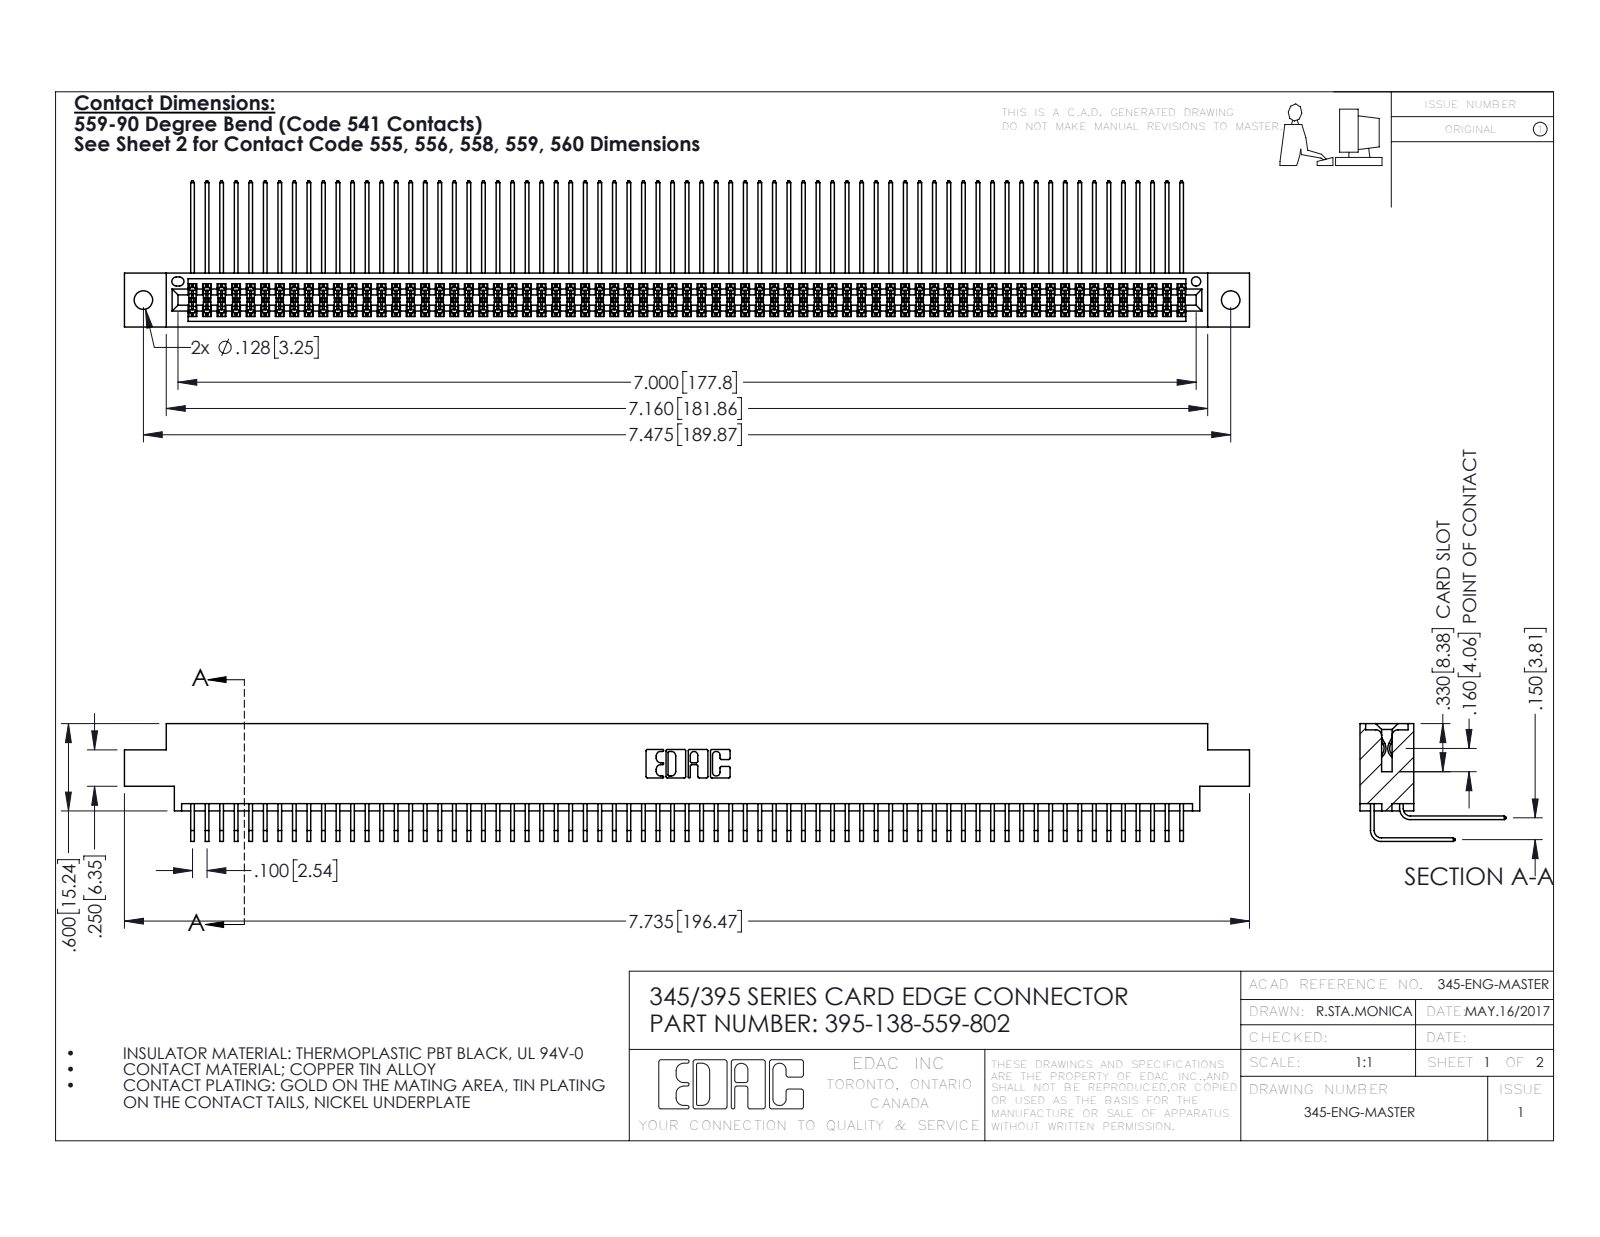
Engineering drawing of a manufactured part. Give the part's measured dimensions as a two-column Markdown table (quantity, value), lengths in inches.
| quantity | value |
| --- | --- |
| part name | 345 Part_0.170 Offset - 0.128 Dia; 395-138-559-802; 345-292-001_558 559 Tail - 1; 345-292-001_559 Tail - 2 |
| STEP written by | SolidWorks 2016 (CONFIG_CONTROL_DESIGN) |
| units | inches |
| bodies | 139 solids, 7306 faces (4914 planar, 2392 cylindrical, 0 other) |
| overall size | 7.735 × 1.005 × 0.809 |
| volume | 1.219 in³ |
| surface area | 52.19 in² |
| round holes (diameter × count) | 0.128 × 2, 0.064 × 1 |
| partial cylindrical surfaces (radius × count) | 0.006 × 275, 0.01 × 22, 0.007 × 6, 0.031 × 6, 0.026 × 3, 0.014 × 2, 0.019 × 2, 0.022 × 2 |
| main face-to-face distances | 0.072, 0.298, 0.37, 0.2, 0.098, 0.272, 0.025, 0.225, 0.175, 0.15 |
| hole center spacings | 0.27, 7.239, 7.475 |
